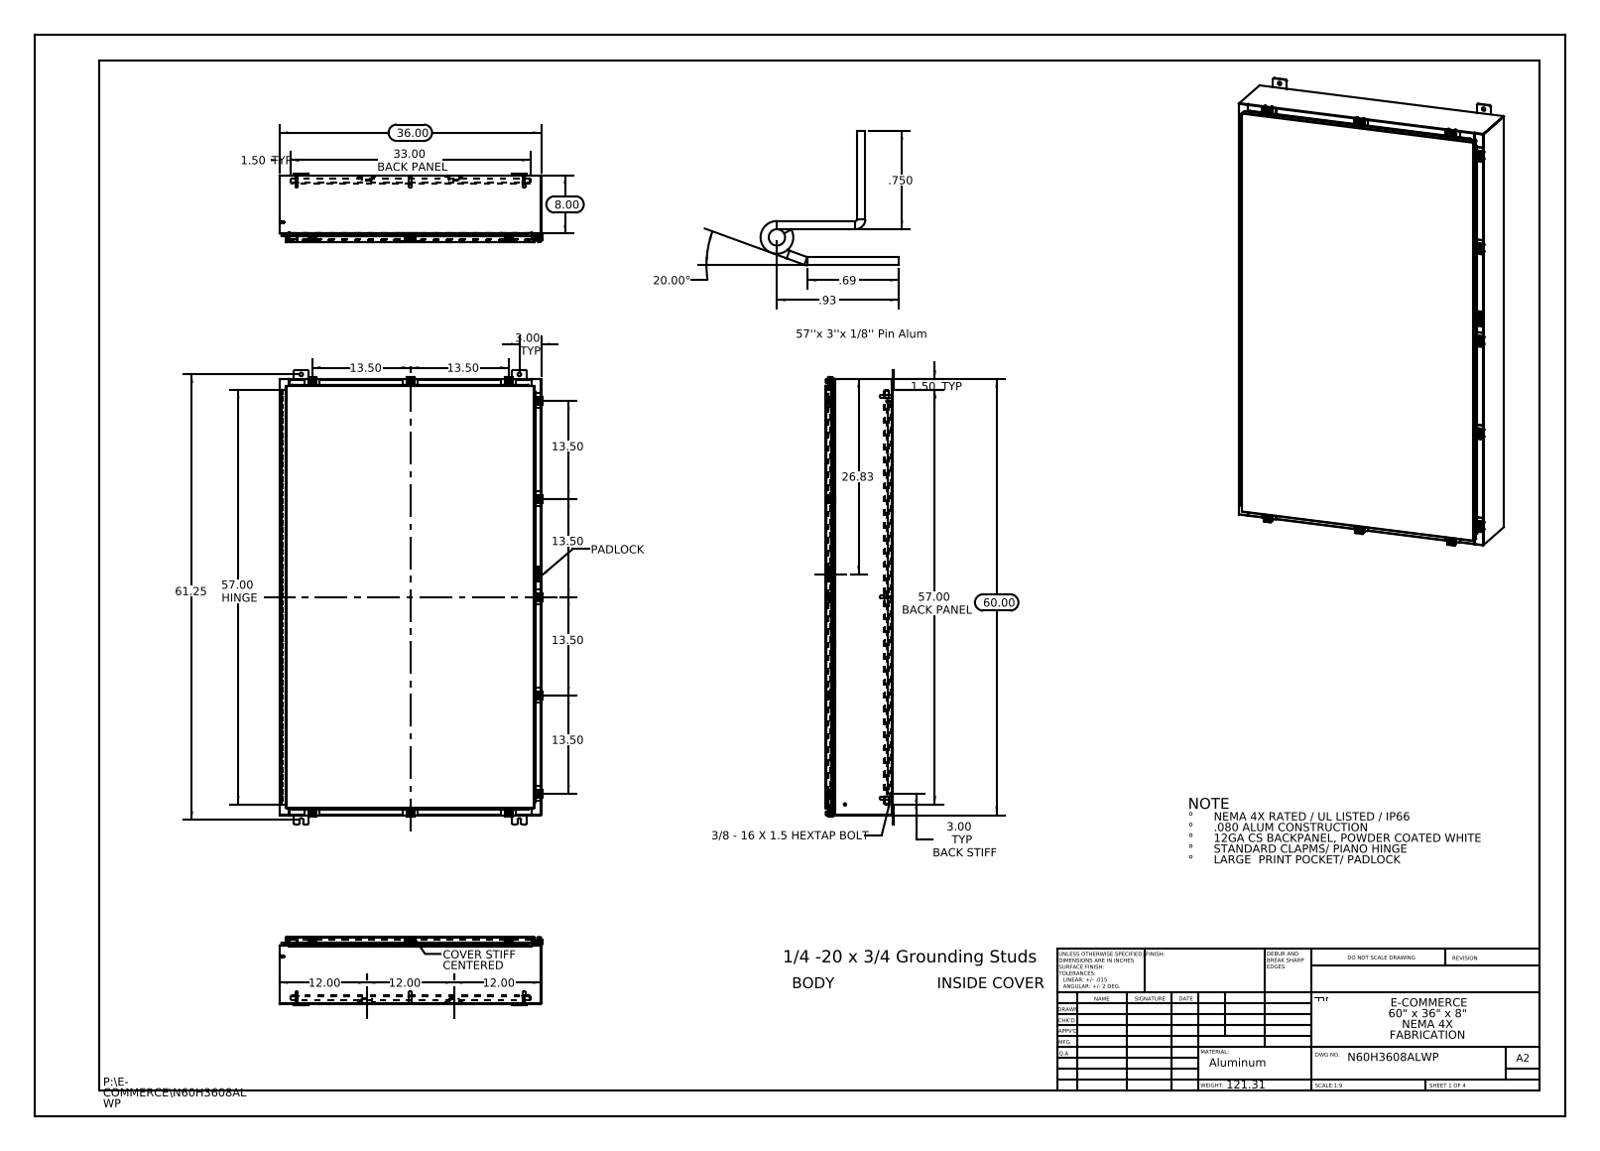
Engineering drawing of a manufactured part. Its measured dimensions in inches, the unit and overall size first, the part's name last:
Units: inches
Overall size (bounding box): 62.5 × 36.211 × 9.389
Round holes (diameter × count): ⌀0.5 ×12, ⌀0.213 ×11, ⌀0.26 ×11, ⌀0.25 ×8, ⌀0.125 ×2, ⌀0.125 ×1
Round bosses / shafts (diameter × count): ⌀0.25 ×12, ⌀0.5 ×11, ⌀0.399 ×11, ⌀0.625 ×8, ⌀0.375 ×8, ⌀0.33 ×8, ⌀0.157 ×8, ⌀0.14 ×8
Partial cylindrical surfaces — rounded edges, fillets, slot ends (radius × count): R0.06 ×50, R0.013 ×39, R0.088 ×33, R0.19 ×24, R0.12 ×22, R0.141 ×22, R0.05 ×17, R0.08 ×16
Main face-to-face distances: 0.075, 9.126, 9.051, 0.104, 9.201, 1, 8.126, 1.075, 8.051, 1.179
Hole centre spacings: 13.5, 13.663, 2.225, 27, 27.625, 29.802, 41.709, 57.39
Volume: 738.9 in³ · Surface area: 18 321 in²
Bodies: 89 solids, 3554 faces (1796 planar, 1506 cylindrical, 252 other)
Part name (STEP PRODUCT): N60H3608ALWP Clamp Assembly; N60H3608ALWP; N60H3608ALWP Mounting Studs; N60H3608ALWP Backpanel (+8 more)
STEP written by: SolidWorks 2013 (CONFIG_CONTROL_DESIGN)
